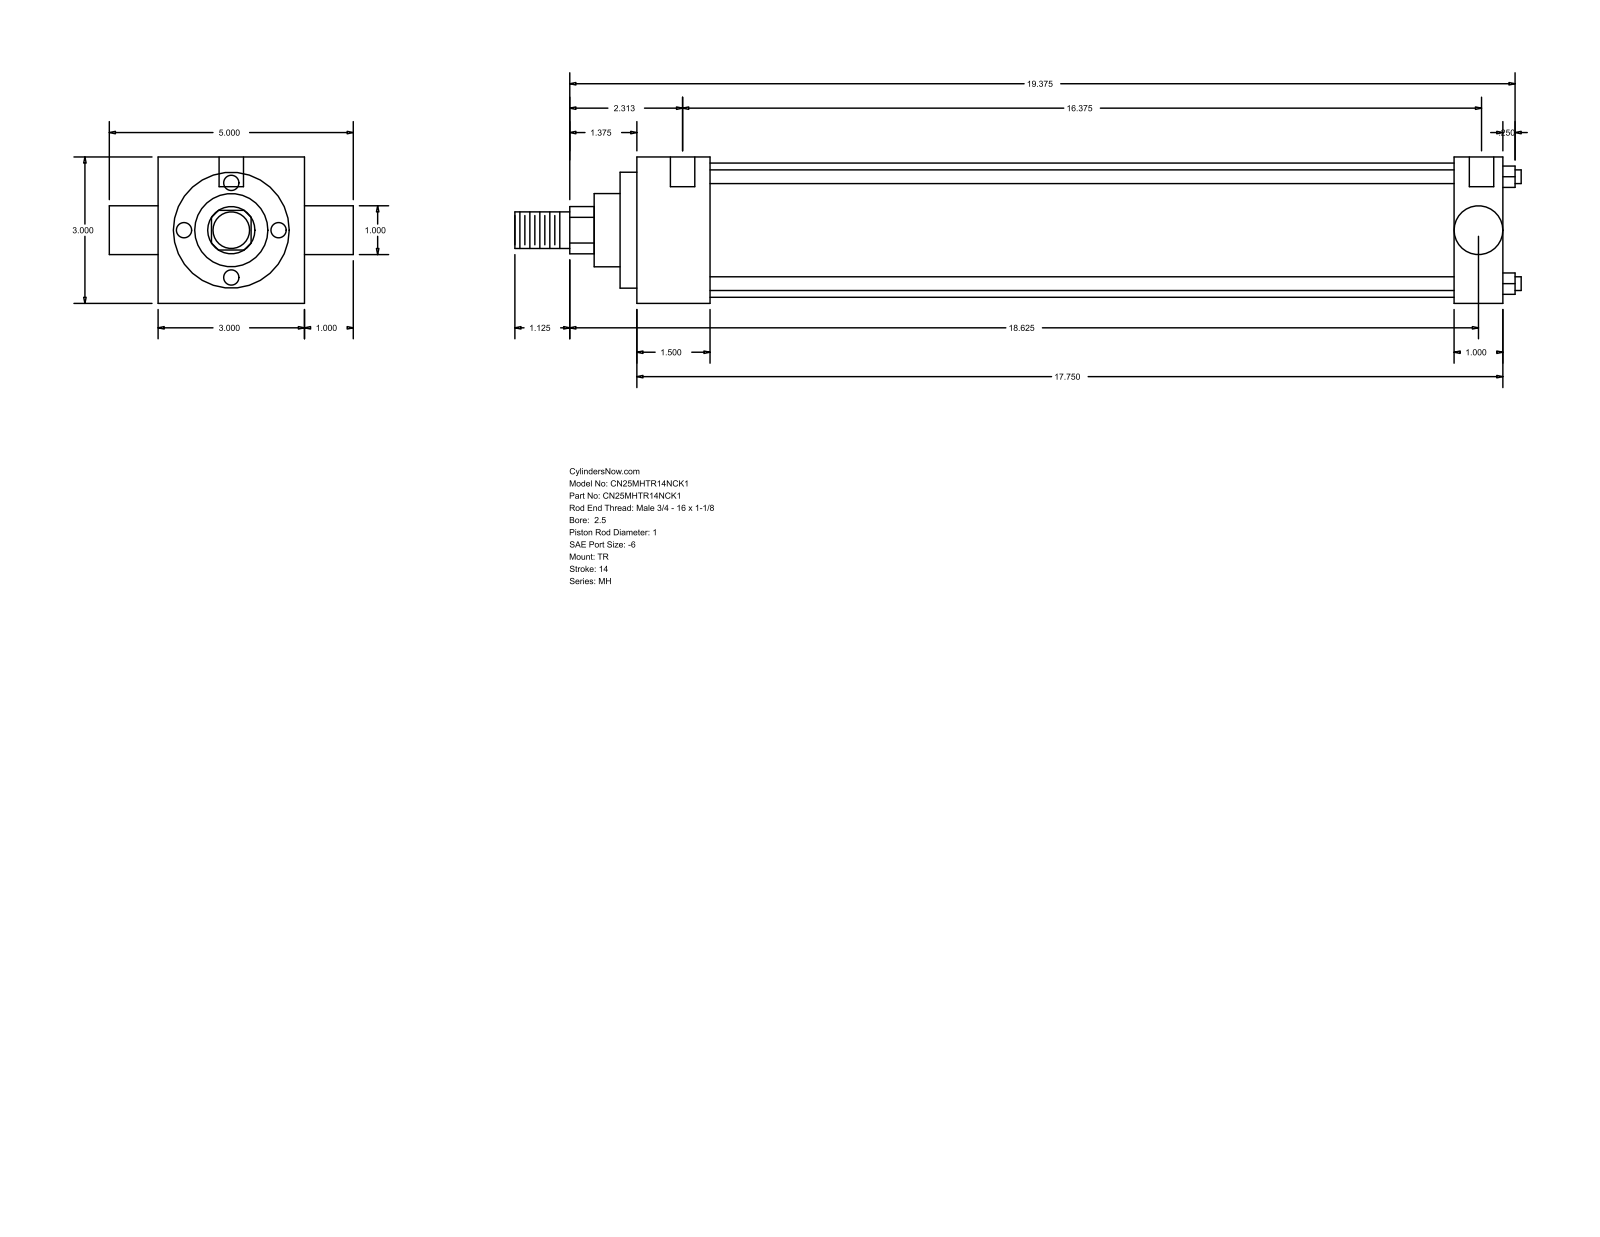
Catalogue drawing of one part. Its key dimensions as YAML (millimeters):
part_name: "MH_TR__0250_1"
step_written_by: "GSSL Pune (CONFIG_CONTROL_DESIGN)"
units: millimeters
bodies: {solids: 0, faces: 86, planar: 61, cylindrical: 25, other: 0}
overall_size: [523.88, 127, 76.2]
round_holes:
  - {diameter: 5.56, count: 3}
  - {diameter: 12.7, count: 2}
round_bosses_or_shafts:
  - {diameter: 7.14, count: 4}
  - {diameter: 69.85, count: 1}
  - {diameter: 60.33, count: 1}
  - {diameter: 38.1, count: 1}
  - {diameter: 25.4, count: 1}
  - {diameter: 25.35, count: 1}
  - {diameter: 19.05, count: 1}
partial_cylinders:
  - {radius: 12.29, count: 1}
face_to_face_distances: [76.2, 450.85, 25.39, 38.11, 412.74, 425.46, 387.35, 8.73, 46.84, 434.19]
hole_center_spacings: [3.18, 4.76, 415.92, 419.1, 420.68, 423.86]
